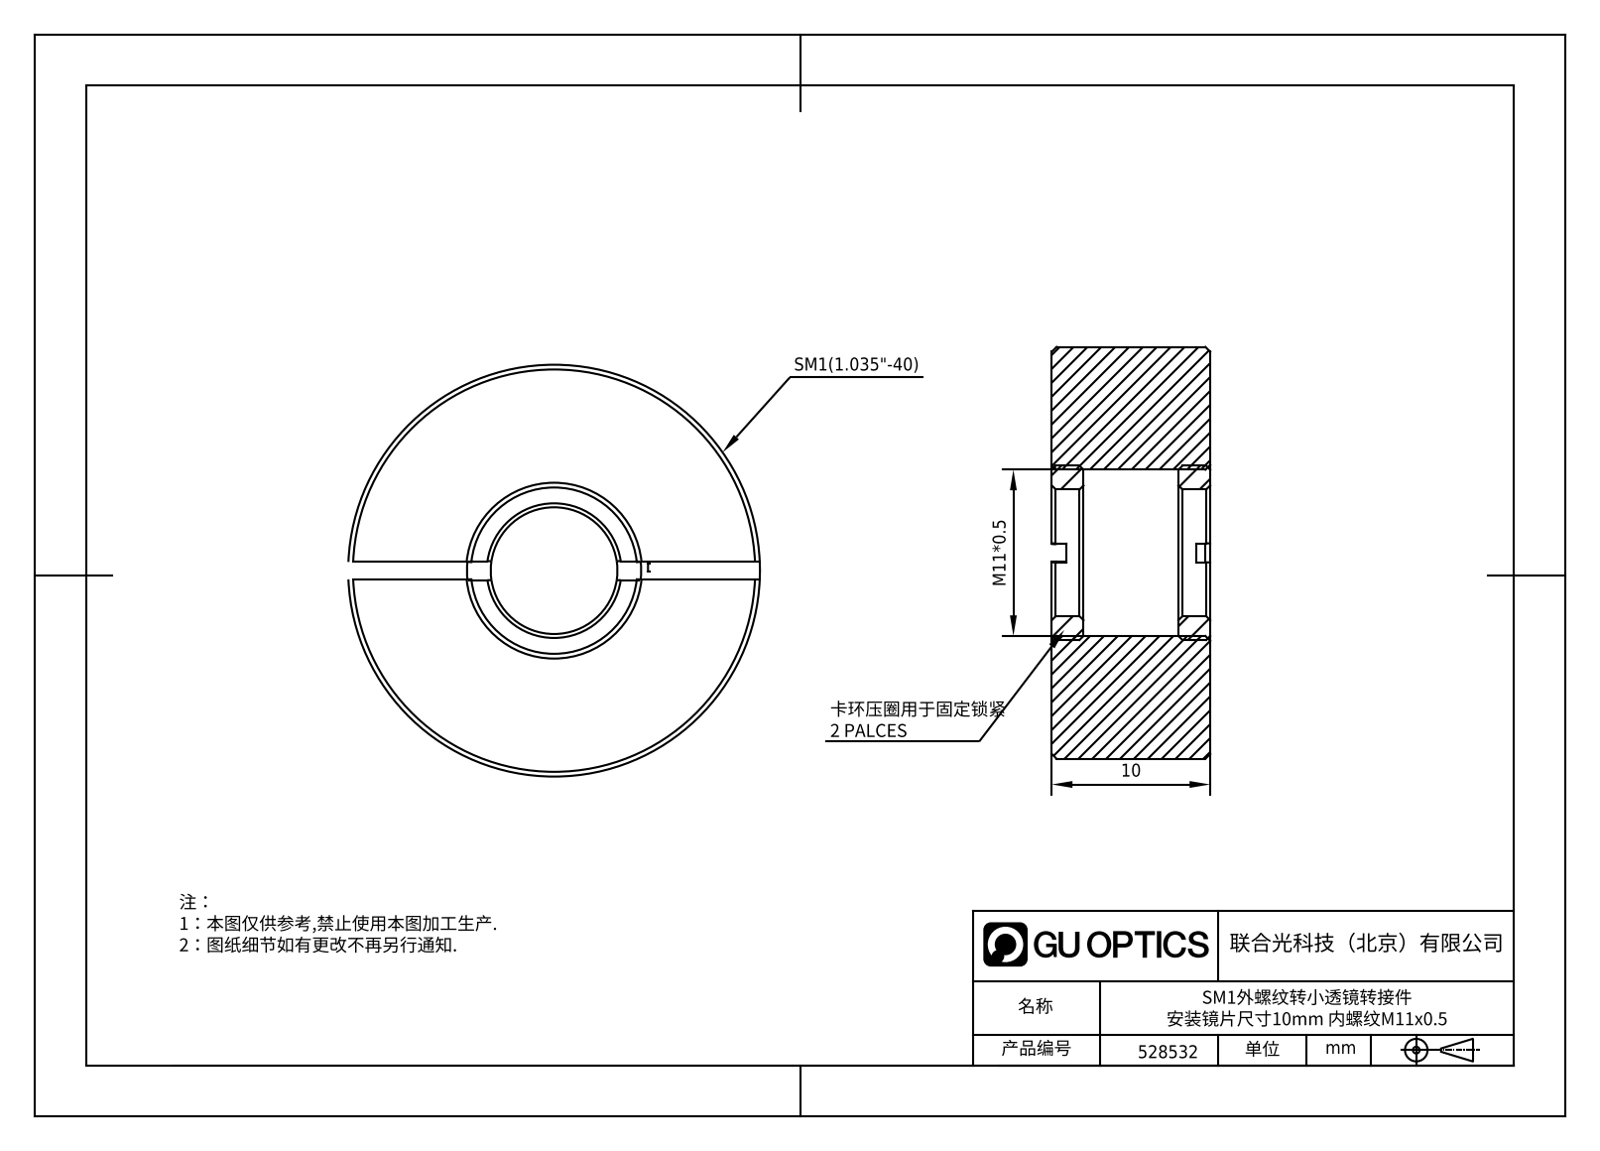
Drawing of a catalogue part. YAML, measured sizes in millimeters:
part_name: "528532"
step_written_by: "SolidWorks 2020 (CONFIG_CONTROL_DESIGN)"
units: millimeters
bodies: {solids: 3, faces: 51, planar: 27, cylindrical: 6, other: 18}
overall_size: [26, 26, 10]
volume: 4582
surface_area: 2408
round_holes:
  - {diameter: 8, count: 1}
  - {diameter: 10.5, count: 1}
round_bosses_or_shafts:
  - {diameter: 26, count: 1}
  - {diameter: 11, count: 1}
face_to_face_distances: [10, 2, 8, 1, 6, 1.1, 9, 7, 1.15, 0.9]
